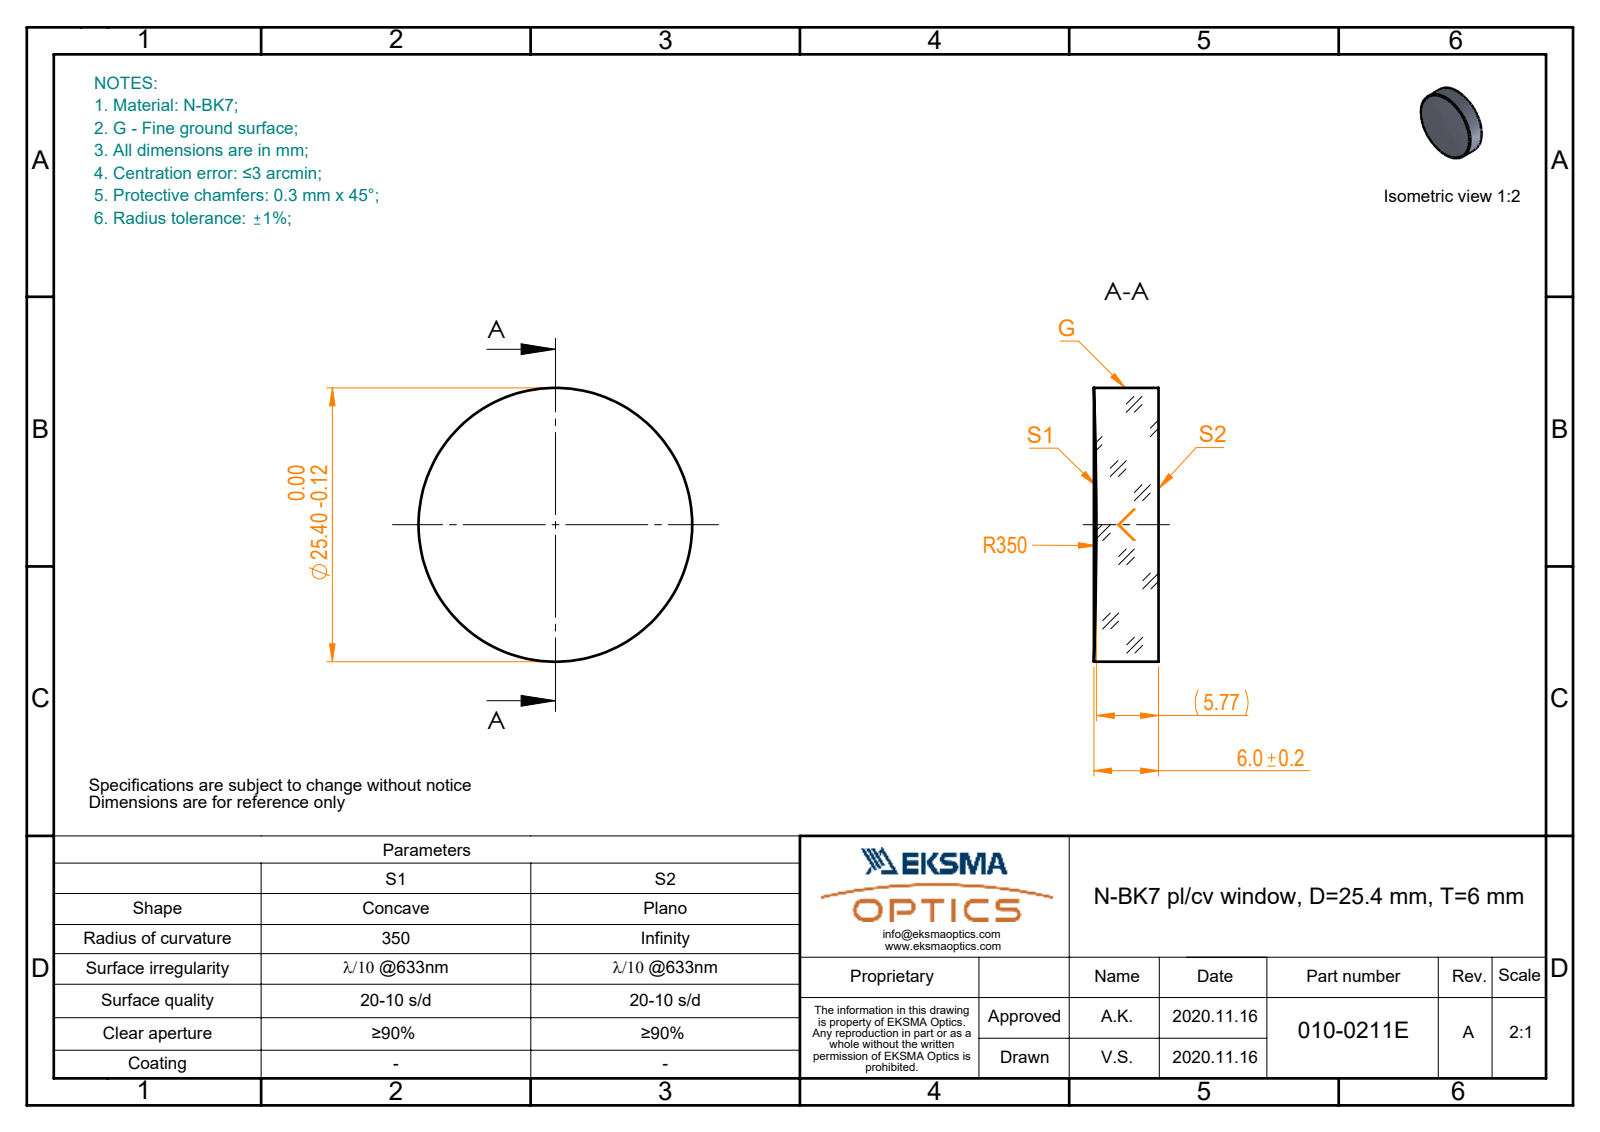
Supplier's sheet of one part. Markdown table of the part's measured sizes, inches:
| quantity | value |
| --- | --- |
| part name | 010-0211E_N-BK7_PCV_window |
| STEP written by | SolidWorks 2019 (CONFIG_CONTROL_DESIGN) |
| units | inches |
| bodies | 1 solid, 5 faces (1 planar, 2 cylindrical, 2 other) |
| overall size | 1 × 1 × 0.236 |
| volume | 0.182 in³ |
| surface area | 2.313 in² |
| round bosses / shafts (diameter × count) | 1 × 1 |
